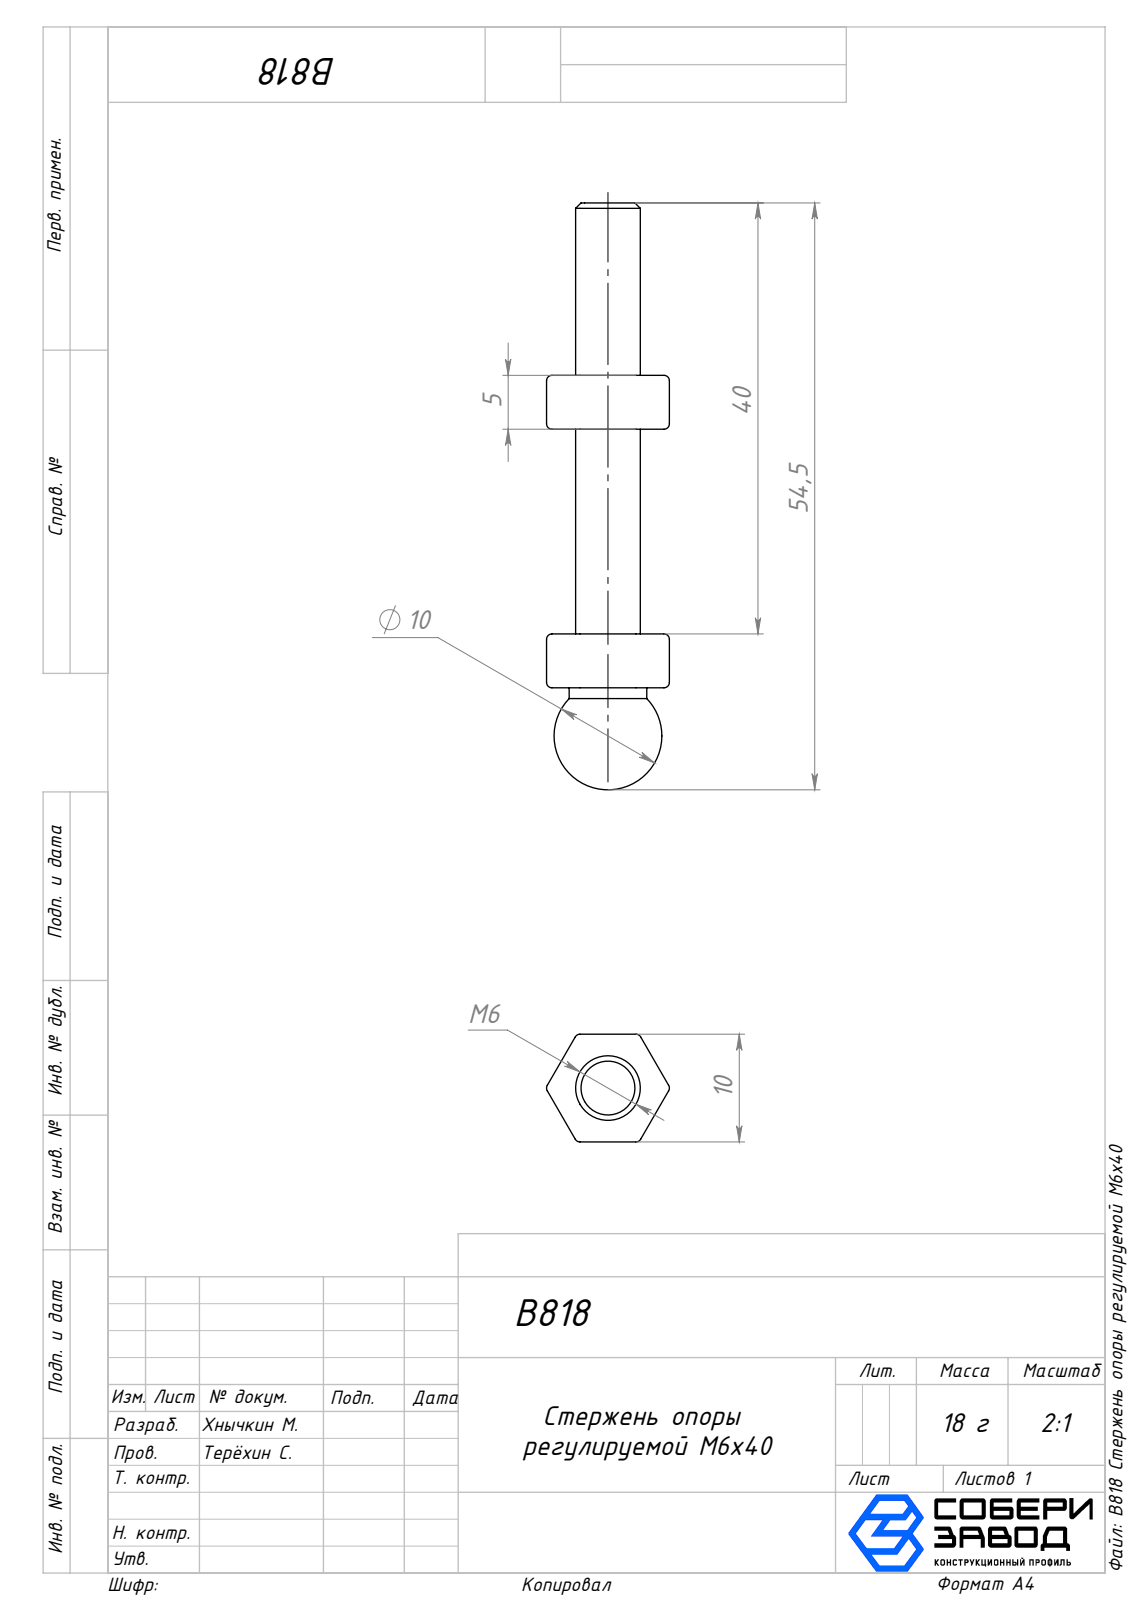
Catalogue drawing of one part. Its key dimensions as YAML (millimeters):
part_name: "Гайка_00; Стержень_00; B818 Стержень опоры регулируемой М6х40"
step_written_by: "SolidWorks 2025 (AUTOMOTIVE_DESIGN)"
units: millimeters
bodies: {solids: 2, faces: 92, planar: 17, cylindrical: 42, other: 33}
overall_size: [54.47, 11.39, 10]
volume: 2416
surface_area: 1686
round_holes:
  - {diameter: 5, count: 1}
round_bosses_or_shafts:
  - {diameter: 7.2, count: 1}
  - {diameter: 6, count: 1}
partial_cylinders:
  - {radius: 0.5, count: 30}
face_to_face_distances: [10, 5, 24, 19, 29, 45, 40, 21, 16]
